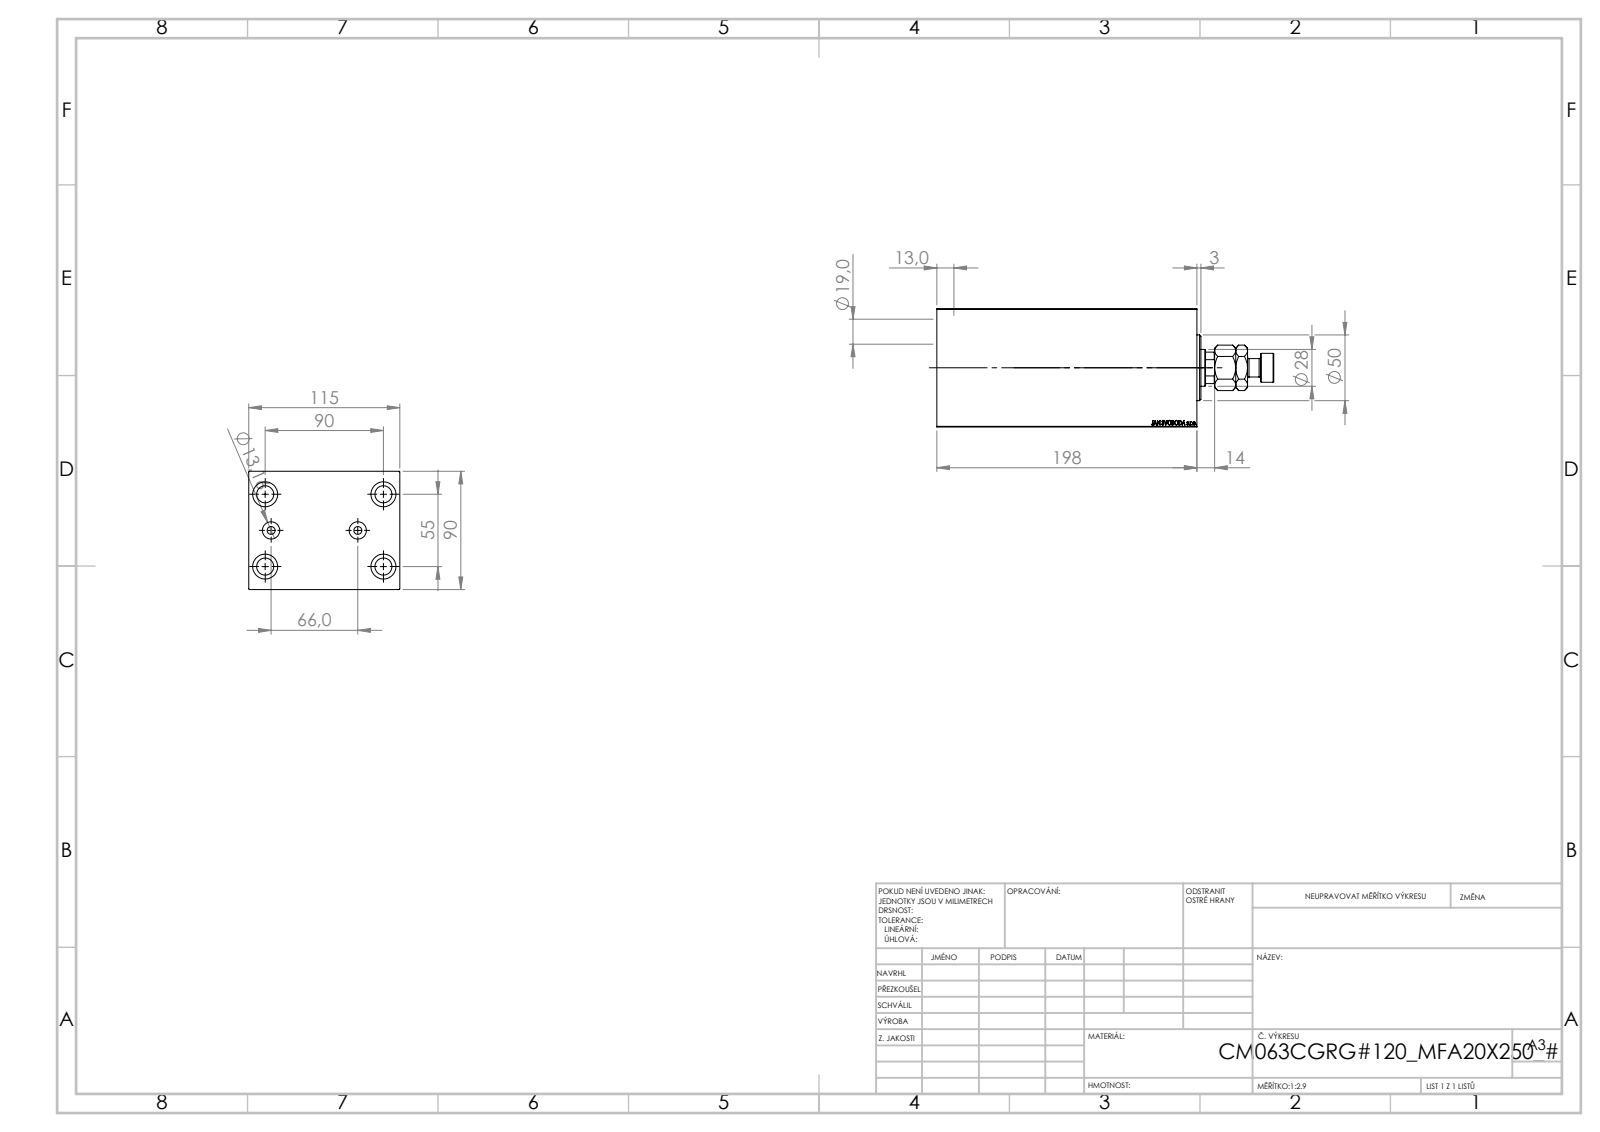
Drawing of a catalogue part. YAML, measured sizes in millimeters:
part_name: "MFA; V450CM_C_Body; V450CM_VC_B; V450CM_C_VCP"
step_written_by: "SolidWorks 2019 (CONFIG_CONTROL_DESIGN)"
units: millimeters
bodies: {solids: 4, faces: 913, planar: 425, cylindrical: 62, other: 426}
overall_size: [256.5, 115, 90]
volume: 1646000
surface_area: 224478
round_holes:
  - {diameter: 13, count: 4}
  - {diameter: 19, count: 4}
  - {diameter: 6, count: 2}
  - {diameter: 13.16, count: 2}
  - {diameter: 18.5, count: 1}
  - {diameter: 28, count: 1}
  - {diameter: 31.5, count: 1}
  - {diameter: 63, count: 1}
  - {diameter: 65, count: 1}
  - {diameter: 72, count: 1}
round_bosses_or_shafts:
  - {diameter: 50, count: 1}
  - {diameter: 22, count: 1}
  - {diameter: 14, count: 1}
partial_cylinders:
  - {radius: 13.5, count: 1}
face_to_face_distances: [90, 115, 198, 17.5, 180.5, 29.3, 151.2, 168.7, 149.3, 120]
hole_center_spacings: [30, 52.74, 82.71, 33, 55, 90, 105.48, 66]
